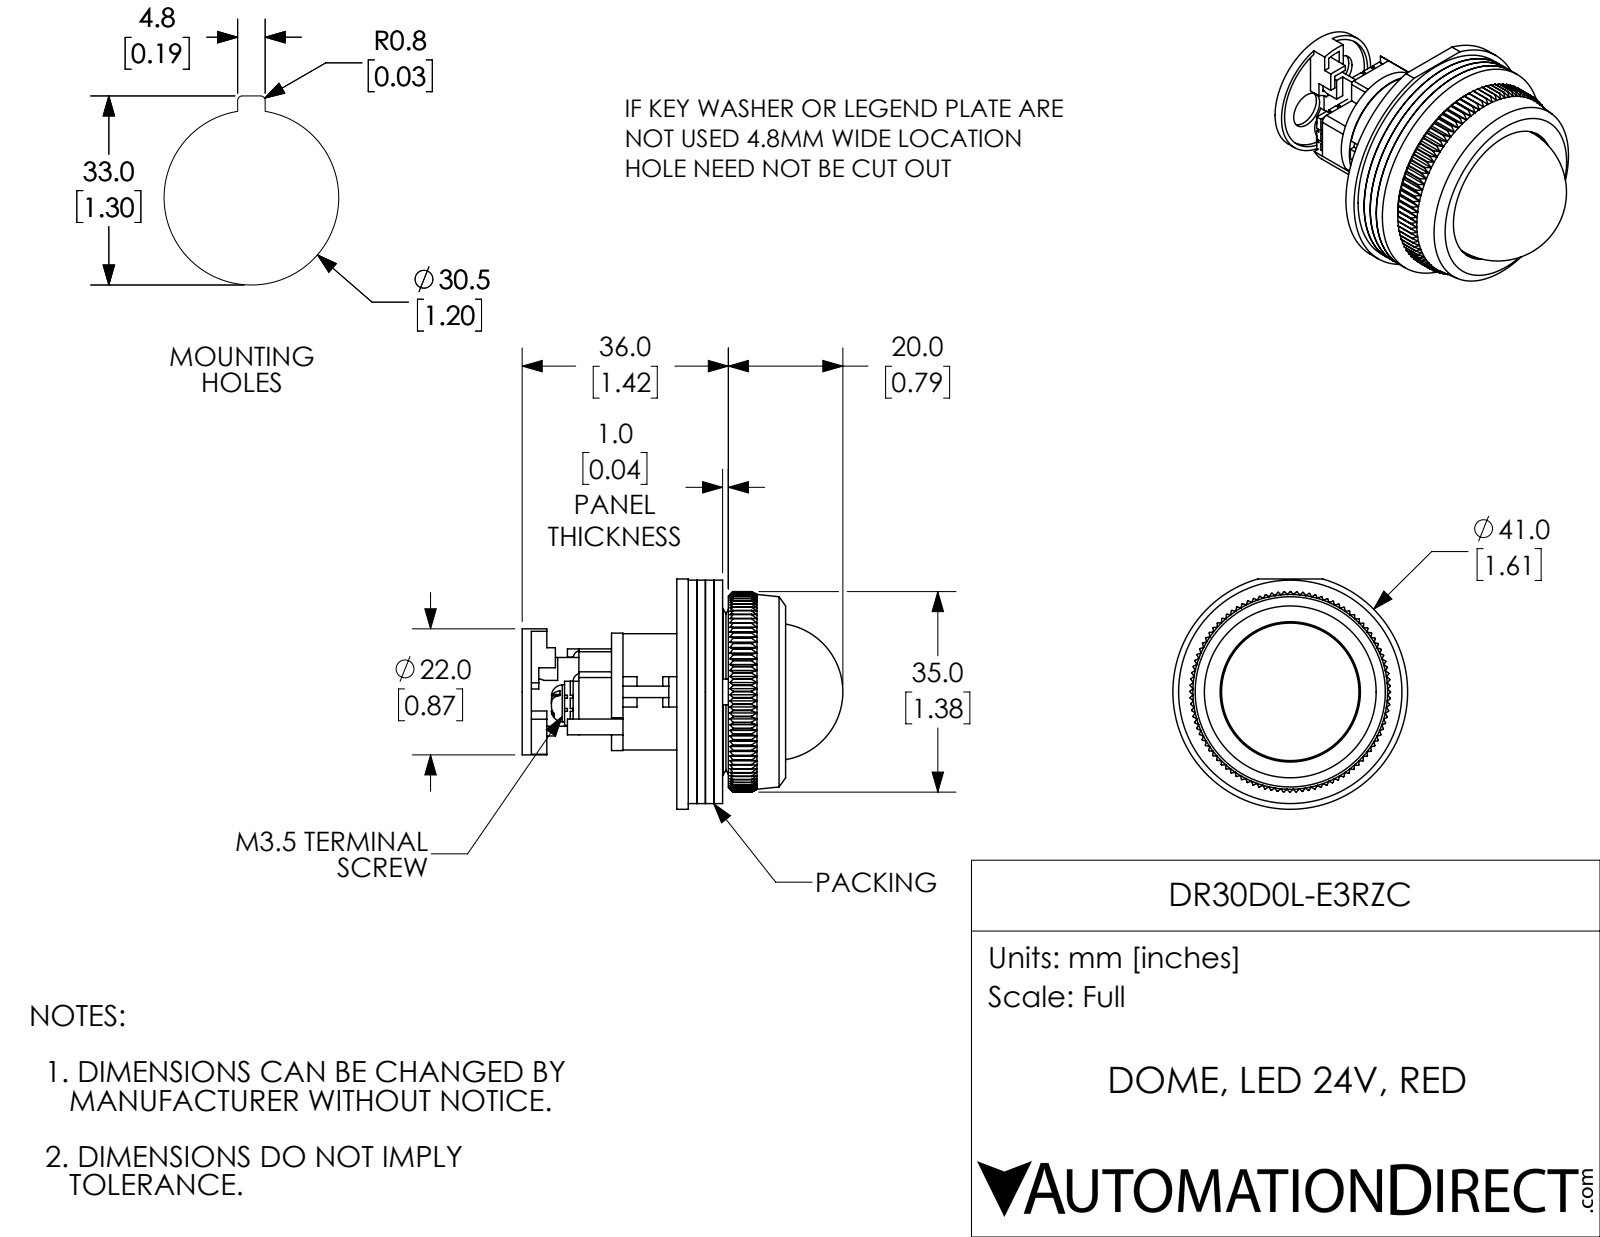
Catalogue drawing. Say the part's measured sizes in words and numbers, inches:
The part is named "DR30D0L-E3RZC". Its 3-D file was written by "SolidWorks 2017 (AUTOMOTIVE_DESIGN)". It is 16 solids with 1350 faces: 770 planar, 336 cylindrical and 244 other. Overall it measures 2.203 by 1.614 by 1.583 inches. Its volume is 1.045 cubic inches and its surface area 37.94 square inches. Round holes: 2 of diameter 0.118, 2 of diameter 0.138, 2 of diameter 0.252, 1 of diameter 0.362, 1 of diameter 0.461, 1 of diameter 0.543, 1 of diameter 0.563, 1 of diameter 0.583, 1 of diameter 0.63, 1 of diameter 0.709, 1 of diameter 0.72, 1 of diameter 0.787. Round bosses or shafts: 2 of diameter 0.063, 1 of diameter 1.614, 1 of diameter 1.535, 1 of diameter 1.16, 1 of diameter 0.945, 1 of diameter 0.858, 1 of diameter 0.819, 1 of diameter 0.799. Partial cylindrical surfaces (rounded edges, fillets, slot ends): 8 of radius 0.059, 5 of radius 0.01, 5 of radius 0.022, 4 of radius 0.016, 4 of radius 0.055, 2 of radius 0.02, 2 of radius 0.039, 2 of radius 0.146. The main face-to-face distances are 0.059, 0.118, 0.177, 0.039, 0.197, 0.079, 0.315, 0.256, 0.098, 0.236. The hole center spacings are 0.176, 0.185, 0.361, 0.352, 0.37.
